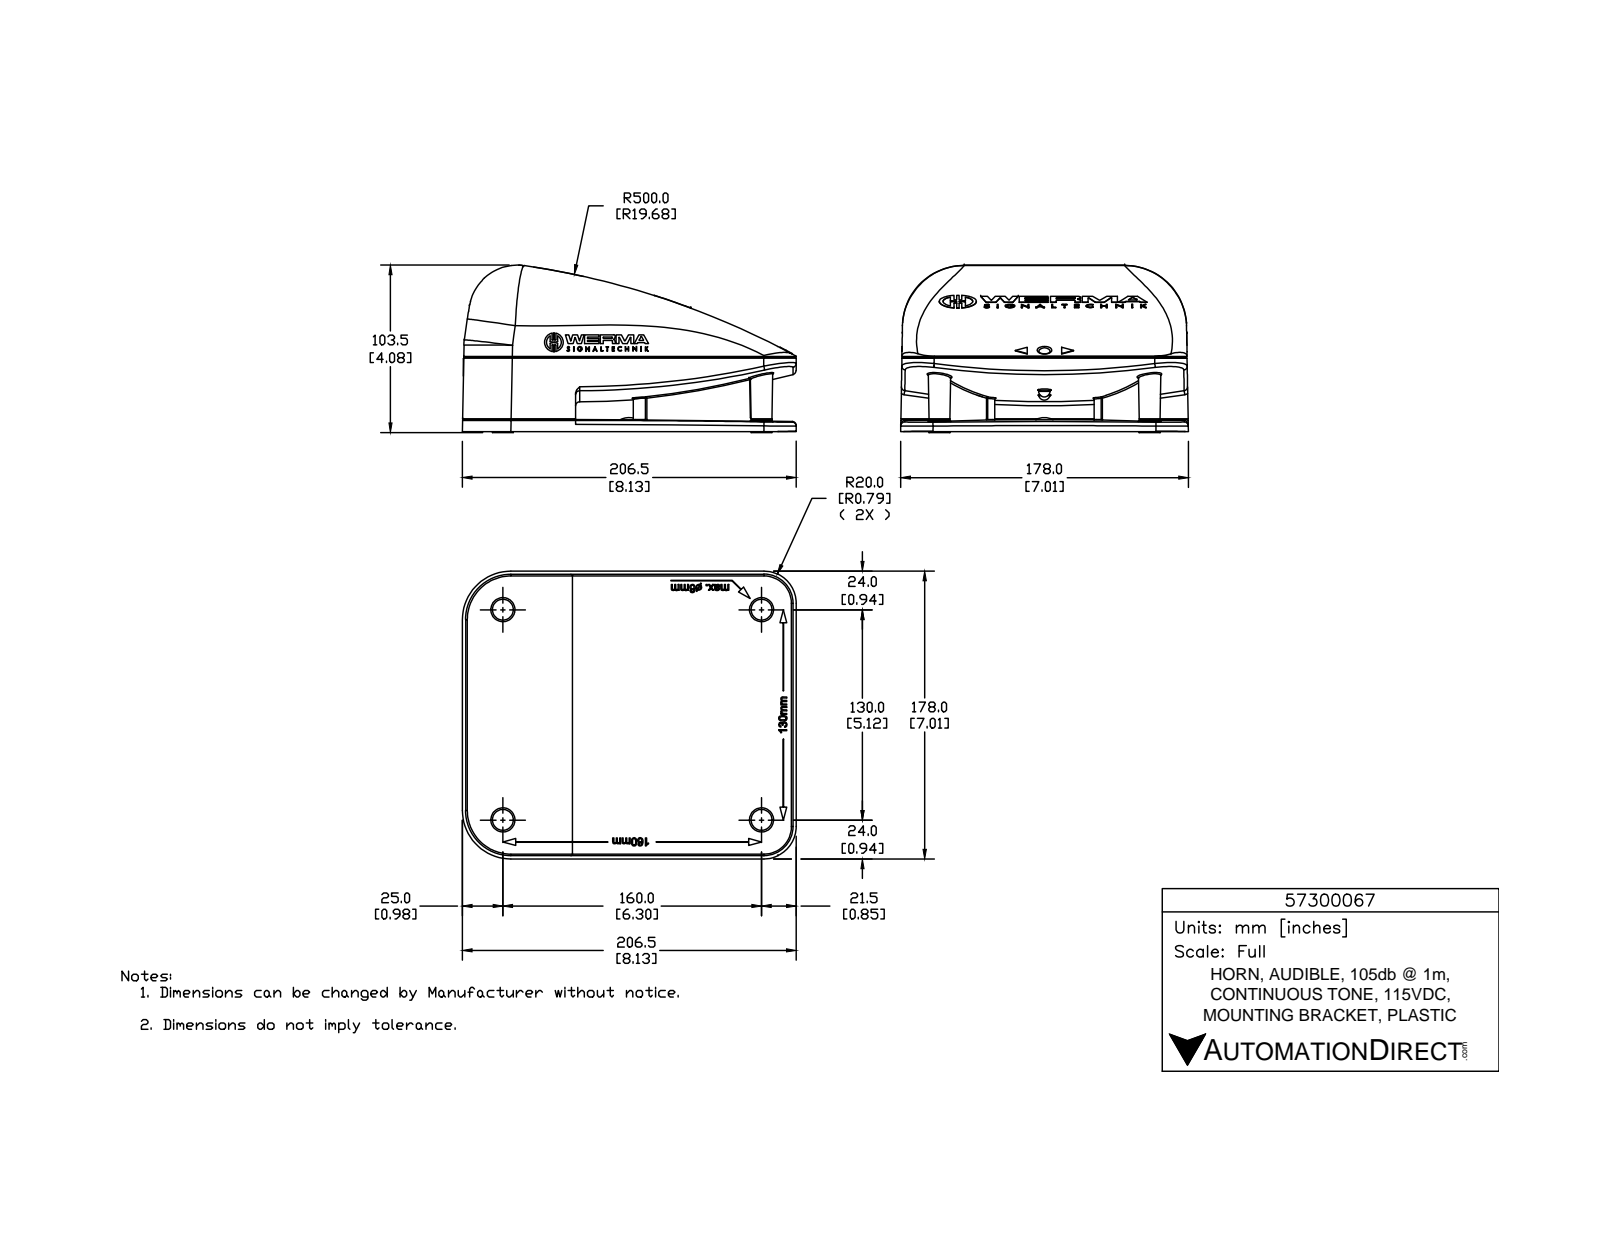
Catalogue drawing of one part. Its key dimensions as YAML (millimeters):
part_name: "57300067"
step_written_by: "SolidWorks 2017 (AUTOMOTIVE_DESIGN)"
units: millimeters
bodies: {solids: 1, faces: 1381, planar: 803, cylindrical: 266, other: 312}
overall_size: [206.5, 182, 103.6]
volume: 2286000
surface_area: 174500
round_holes:
  - {diameter: 2, count: 2}
  - {diameter: 3.2, count: 1}
  - {diameter: 4, count: 1}
  - {diameter: 14.4, count: 1}
  - {diameter: 16, count: 1}
  - {diameter: 22.3, count: 1}
round_bosses_or_shafts:
  - {diameter: 13, count: 2}
  - {diameter: 12.9, count: 2}
  - {diameter: 11.8, count: 2}
  - {diameter: 11.5, count: 2}
  - {diameter: 8.5, count: 2}
  - {diameter: 2.9, count: 2}
  - {diameter: 23, count: 1}
  - {diameter: 5.7, count: 1}
partial_cylinders:
  - {radius: 0.2, count: 6}
  - {radius: 20, count: 6}
  - {radius: 30, count: 6}
  - {radius: 0.4, count: 5}
  - {radius: 1, count: 5}
  - {radius: 0.2, count: 4}
  - {radius: 0.4, count: 4}
  - {radius: 0.4, count: 4}
face_to_face_distances: [5.5, 2, 2, 136.4, 174, 2, 136.5, 68, 204.4, 0.5]
hole_center_spacings: [20.4, 64.8]
